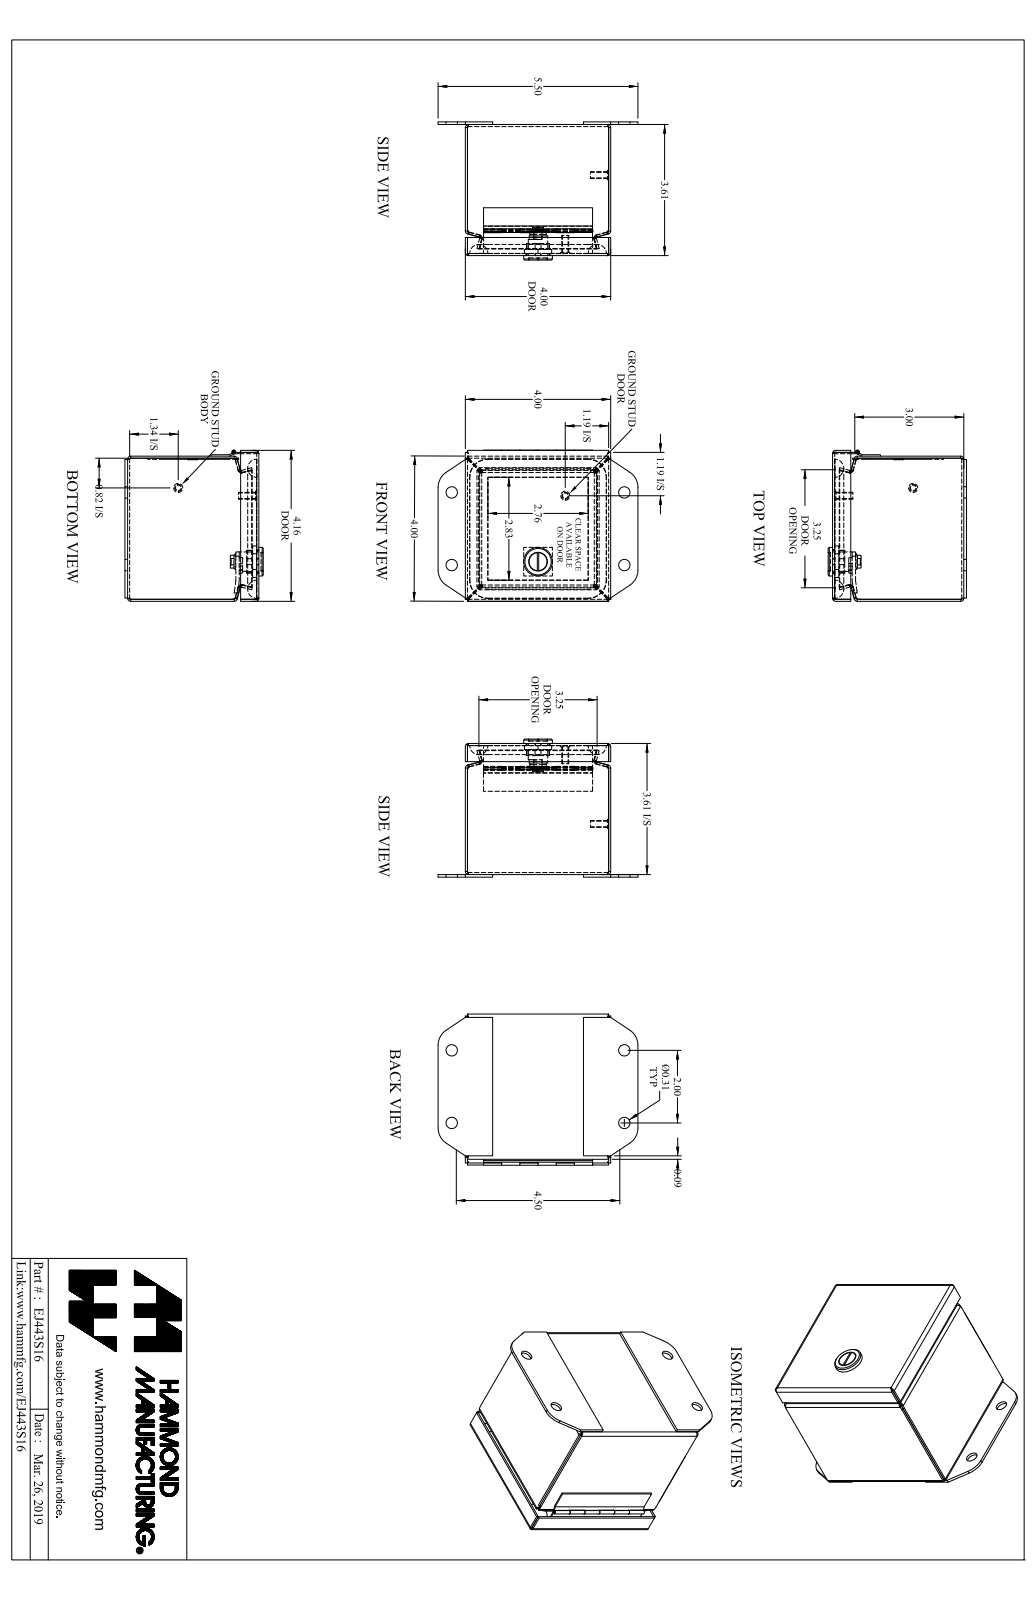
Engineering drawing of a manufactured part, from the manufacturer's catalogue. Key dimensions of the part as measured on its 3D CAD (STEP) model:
Part name (STEP PRODUCT): EJ443S16_Default
STEP written by: SolidWorks 2019 (CONFIG_CONTROL_DESIGN)
Units: inches
Bodies: 11 solids, 438 faces (248 planar, 134 cylindrical, 56 other)
Overall size (bounding box): 5.5 × 4.165 × 3.805
Volume: 7.781 in³ · Surface area: 257.1 in²
Round holes (diameter × count): ⌀0.313 ×4, ⌀0.05 ×1, ⌀0.516 ×1
Round bosses / shafts (diameter × count): ⌀0.25 ×2, ⌀0.19 ×2, ⌀0.788 ×1, ⌀0.535 ×1, ⌀0.496 ×1, ⌀0.435 ×1, ⌀0.1 ×1, ⌀0.045 ×1
Partial cylindrical surfaces — rounded edges, fillets, slot ends (radius × count): R0.029 ×16, R0.086 ×16, R0.281 ×12, R0.25 ×4, R0.499 ×4, R0.5 ×4, R0.06 ×2, R0.03 ×1
Main face-to-face distances: 0.057, 3.943, 3.554, 3.886, 4, 3.611, 3.497, 3.683, 3.626, 0.129
Hole centre spacings: 2, 2.377, 3.046, 4.75, 5.154
